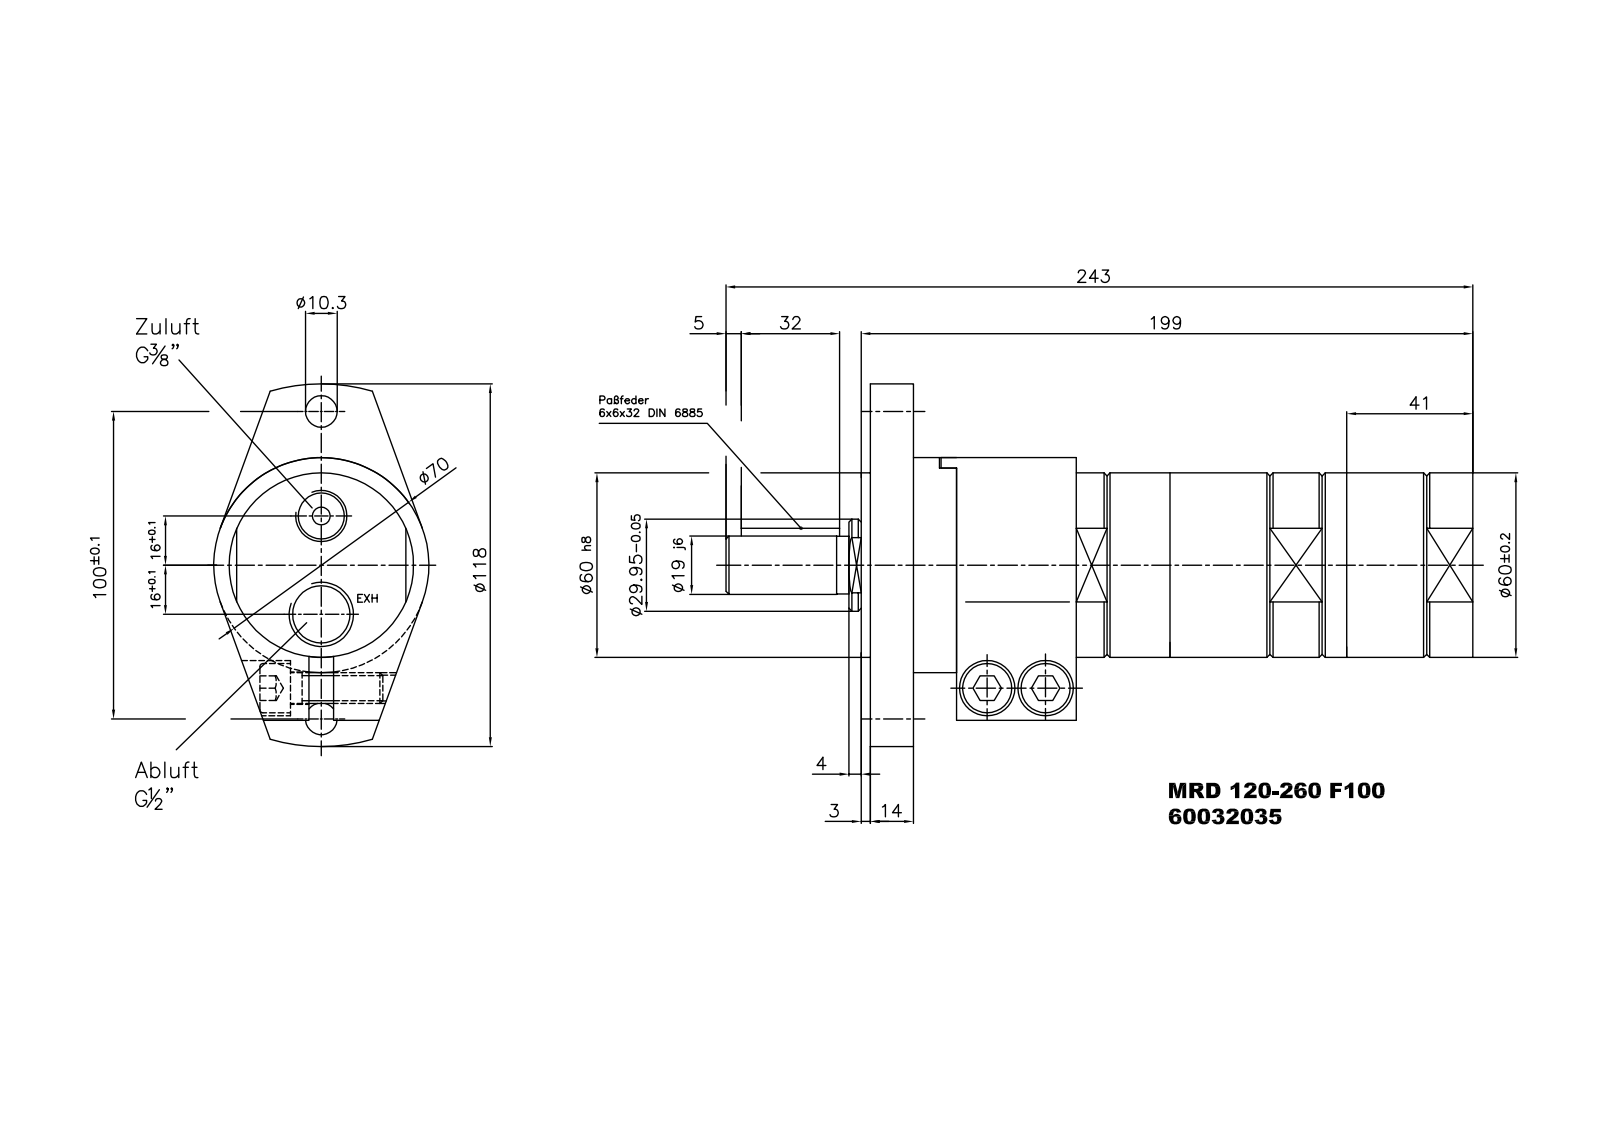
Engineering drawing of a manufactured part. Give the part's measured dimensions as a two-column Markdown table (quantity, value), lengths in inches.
| quantity | value |
| --- | --- |
| part name | MRD 120-9300 F100_60032095 |
| STEP written by | Autodesk Inventor 2014 (AUTOMOTIVE_DESIGN) |
| units | inches |
| bodies | 1 solid, 223 faces (123 planar, 54 cylindrical, 46 other) |
| overall size | 9.567 × 4.646 × 2.756 |
| volume | 42.05 in³ |
| surface area | 117.9 in² |
| round holes (diameter × count) | 0.33 × 2, 0.406 × 2, 0.413 × 2, 0.709 × 2, 0.061 × 1, 0.063 × 1, 0.157 × 1, 0.217 × 1, 0.589 × 1, 0.733 × 1, 1.378 × 1, 2.051 × 1 |
| round bosses / shafts (diameter × count) | 0.63 × 2, 0.394 × 2, 2.756 × 1, 2.362 × 1, 2.244 × 1, 2.172 × 1, 2.047 × 1, 1.575 × 1 |
| partial cylindrical surfaces (radius × count) | 0.118 × 2, 2.323 × 1 |
| main face-to-face distances | 0.551, 7.717, 7.165, 0.669, 0.118, 7.835, 2.76, 2.642, 2.091, 5.075 |
| hole center spacings | 0.63, 1.339, 1.969, 2.598, 0.748, 1.26, 3.937 |
